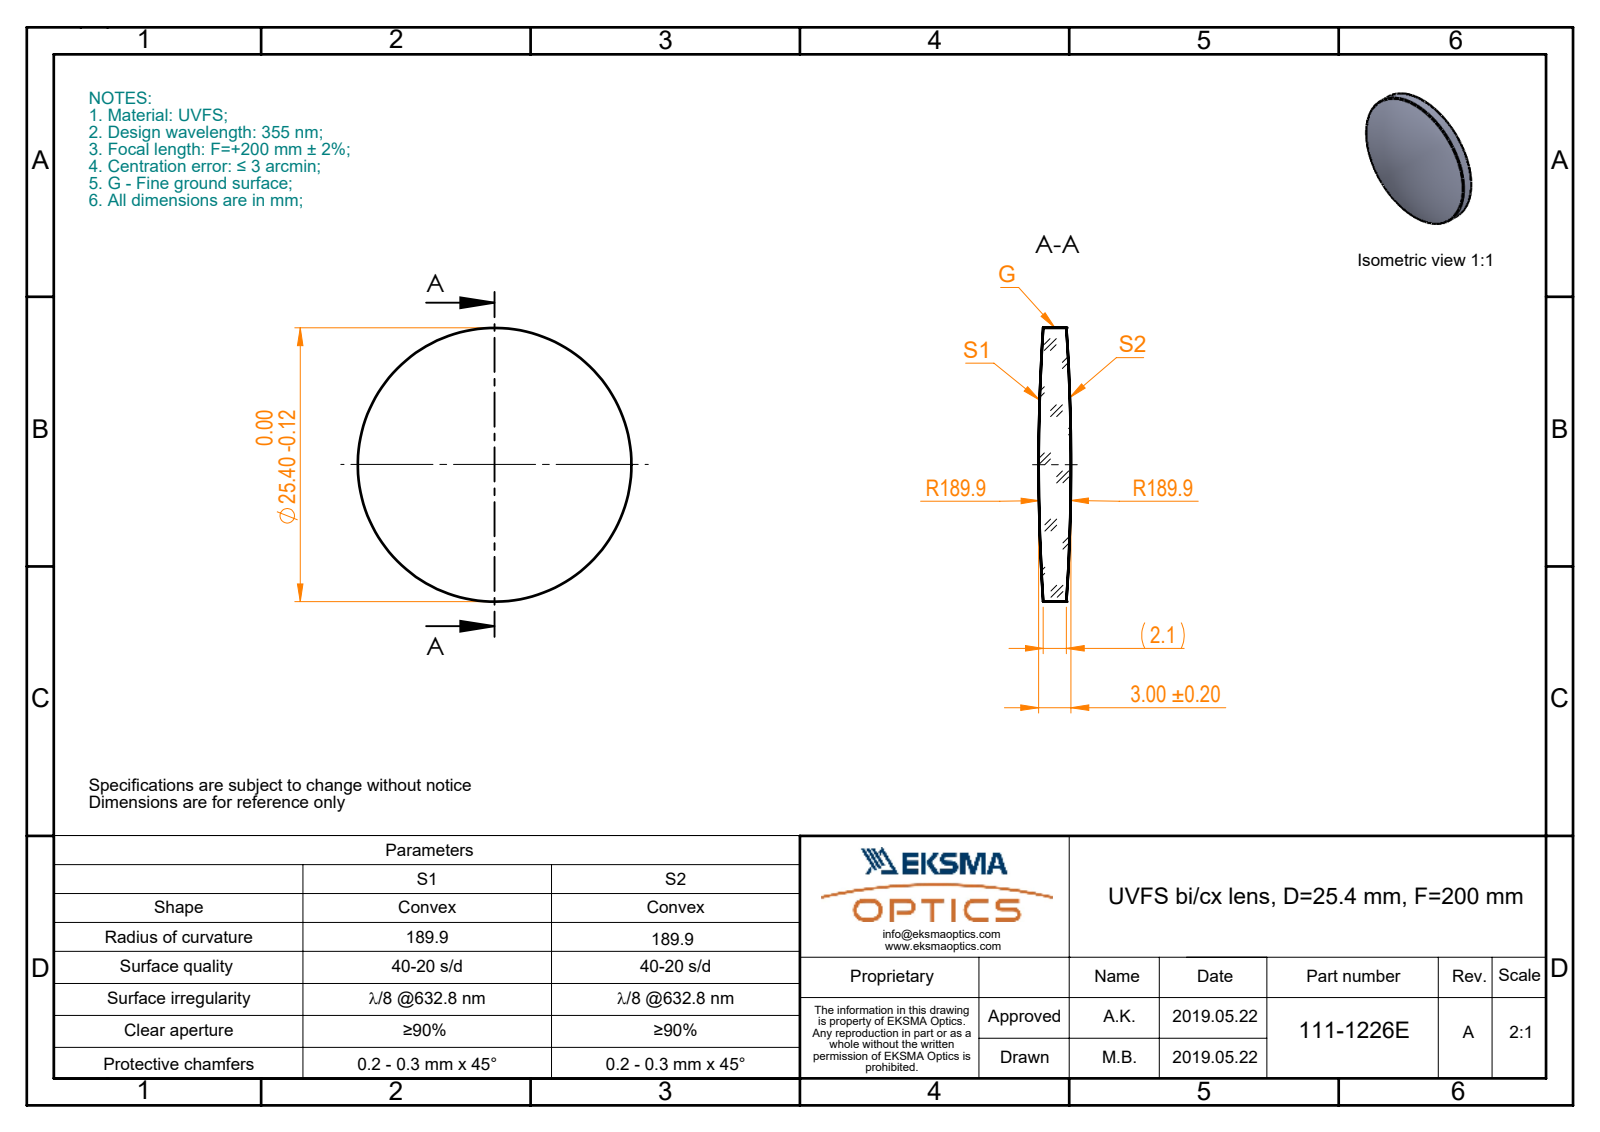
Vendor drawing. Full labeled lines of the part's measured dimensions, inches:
Part name (STEP PRODUCT): 111-1226E UVFS bi-cx 25.4 F200
STEP written by: SolidWorks 2017 (CONFIG_CONTROL_DESIGN)
Units: inches
Bodies: 1 solid, 6 faces (0 planar, 2 cylindrical, 4 other)
Overall size (bounding box): 1 × 1 × 0.118
Volume: 0.08 in³ · Surface area: 1.838 in²
Round bosses / shafts (diameter × count): ⌀1 ×1
